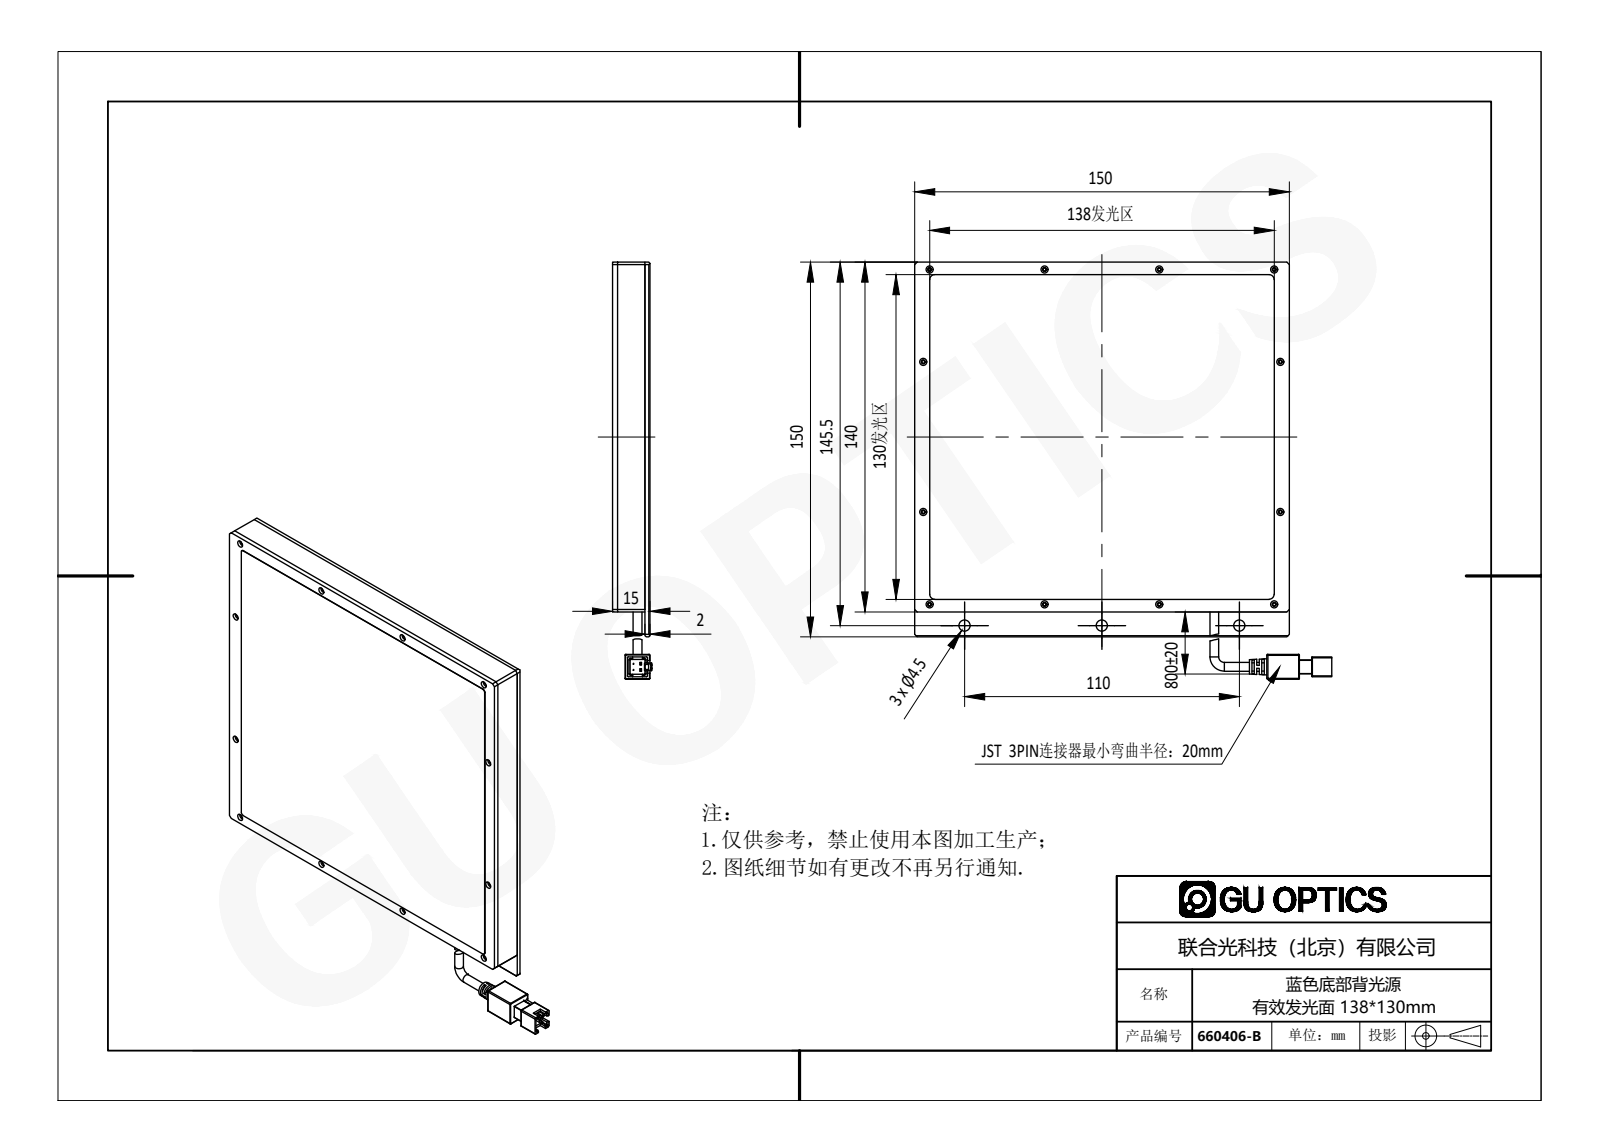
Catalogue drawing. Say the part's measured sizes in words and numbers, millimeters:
The part is named "660406-B". Its 3-D file was written by "SolidWorks 2016 (AUTOMOTIVE_DESIGN)". It is 22 solids with 3021 faces: 2610 planar, 253 cylindrical and 158 other. Overall it measures 167 by 167 by 15.9 millimeters. Its volume is 165 313 cubic millimeters and its surface area 154 286 square millimeters. Round holes: 12 of diameter 1.1, 12 of diameter 1.4, 12 of diameter 1.5, 12 of diameter 1.6, 12 of diameter 2, 12 of diameter 2.2, 12 of diameter 2.8, 3 of diameter 4.5. Round bosses or shafts: 2 of diameter 3.5. Partial cylindrical surfaces (rounded edges, fillets, slot ends): 15 of radius 0.1, 13 of radius 0.2, 12 of radius 0.4, 6 of radius 1, 4 of radius 2, 2 of radius 1.5, 1 of radius 0.3, 1 of radius 0.68. The main face-to-face distances are 2, 11, 13, 15.2, 13.2, 2.2, 4, 9, 11.2, 5. The hole center spacings are 46, 141.68, 37.08, 61, 92, 97.03, 101.49, 108.45.
